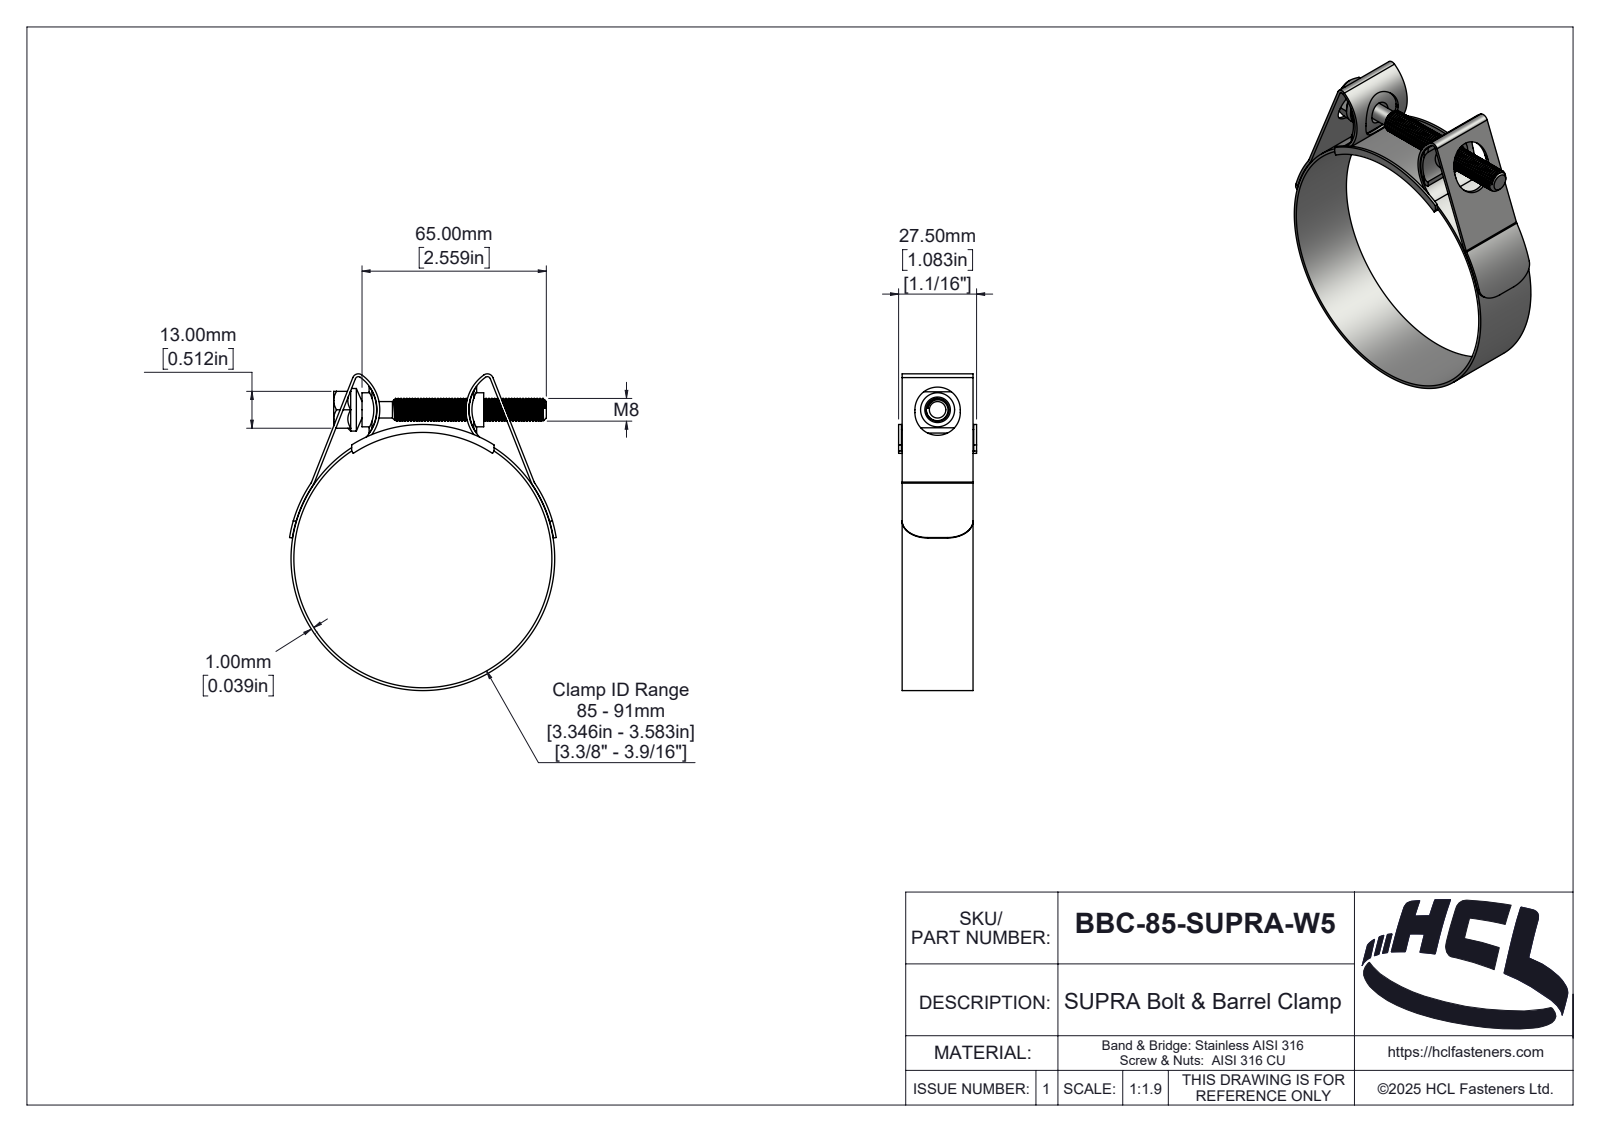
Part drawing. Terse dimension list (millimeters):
name: BBC-85-SUPRA-W5
written by: SolidWorks 2025 (AUTOMOTIVE_DESIGN)
unit: mm
bodies: 5 solids, 349 faces (46 planar, 217 cylindrical, 86 other)
size: 111.65 × 94.03 × 27.5
volume: 16 527 mm³; area: 28 933 mm²
holes: 1× ⌀91
bosses: 1× ⌀93, 1× ⌀15.01, 1× ⌀12, 1× ⌀8, 1× ⌀5.8
rounds: 4× R1, 2× R1.1, 2× R2, 2× R2.1, 2× R3, 2× R8, 2× R12.99, 2× R13.99
face distances: 1, 25, 1.25, 26.25, 26.5, 25.25, 27.5, 13, 2.5, 40.42
